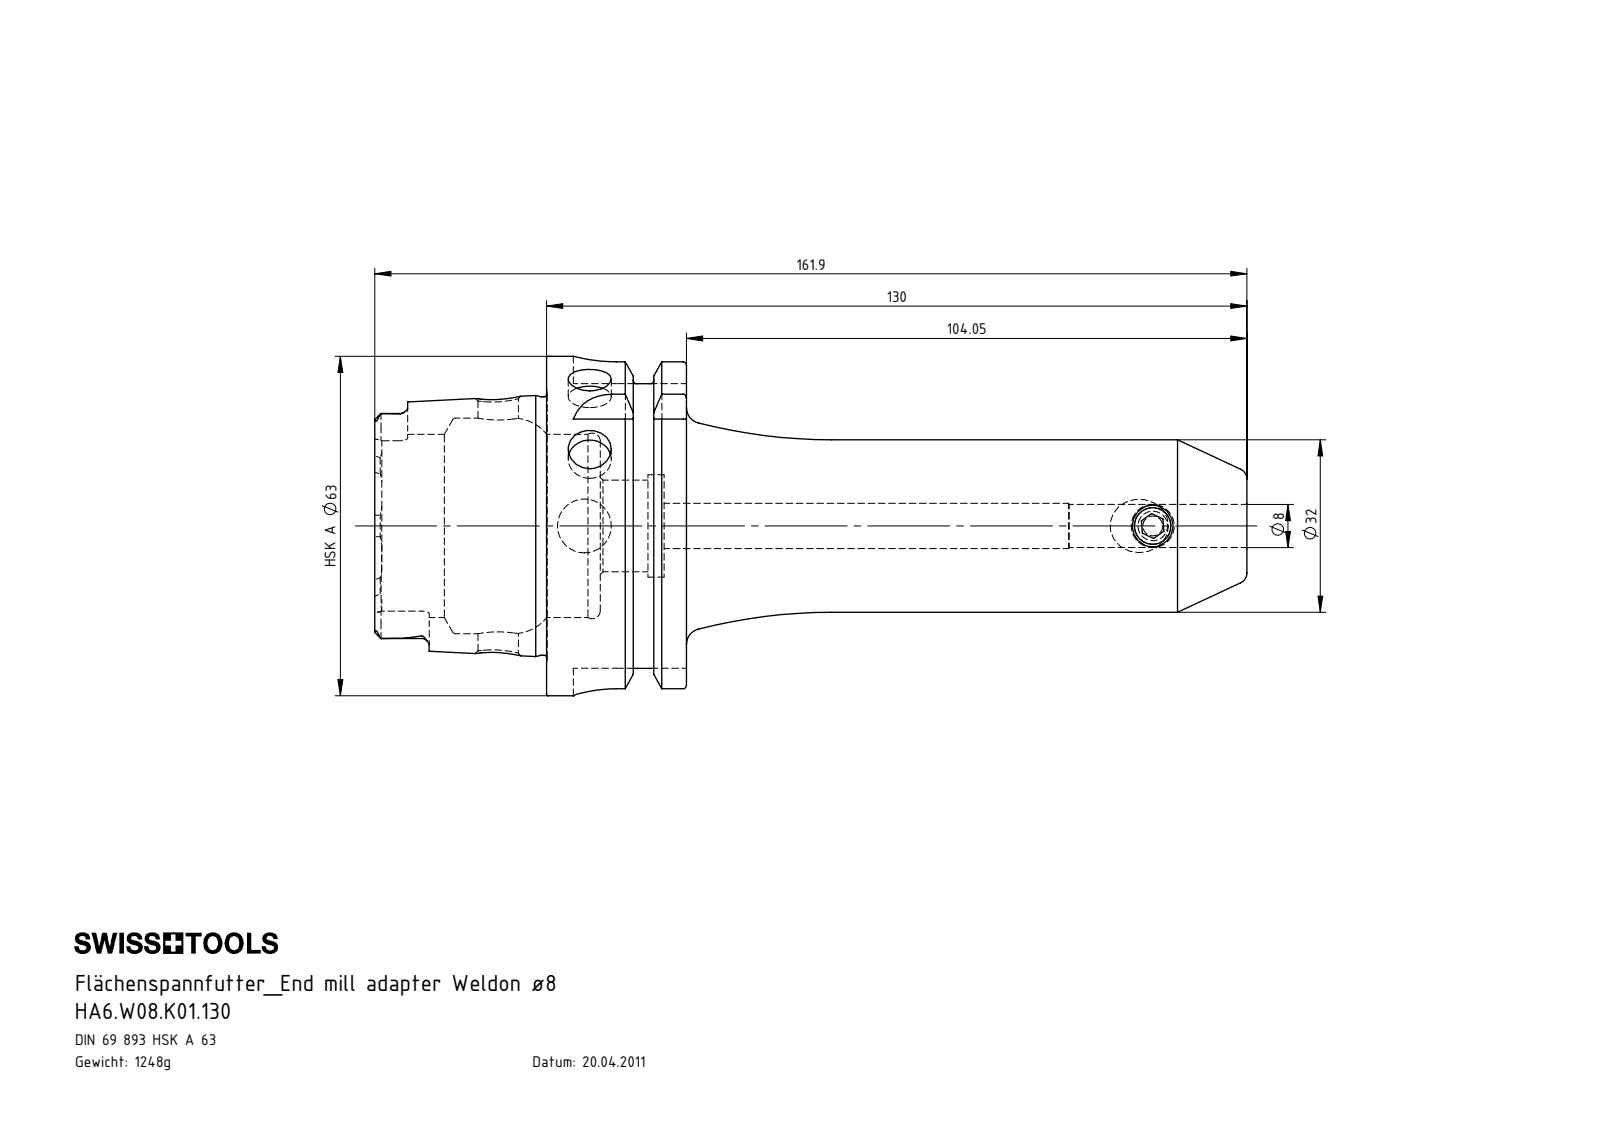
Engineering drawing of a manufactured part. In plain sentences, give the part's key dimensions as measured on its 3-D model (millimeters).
The part is named "HA6-W08.K01.130; W08-ER1.001.010; HA6-W08.K01.130_A_Fertigbearbeitung". Its 3-D file was written by "SolidWorks 2012 (CONFIG_CONTROL_DESIGN)". It is 2 solids with 203 faces: 57 planar, 55 cylindrical and 91 other. Overall it measures 161.9 by 63 by 63 millimeters. Its volume is 159 027 cubic millimeters and its surface area 35 308 square millimeters. Round holes: 3 of diameter 8, 1 of diameter 6.8, 1 of diameter 7.5, 1 of diameter 8.4, 1 of diameter 10, 1 of diameter 17, 1 of diameter 19, 1 of diameter 34, 1 of diameter 40. Round bosses or shafts: 1 of diameter 63, 1 of diameter 54.95, 1 of diameter 47.94, 1 of diameter 32, 1 of diameter 8. Partial cylindrical surfaces (rounded edges, fillets, slot ends): 6 of radius 1.4, 4 of radius 2.88, 4 of radius 8. The main face-to-face distances are 25.95, 16, 9.95, 31.9, 41.85, 57.85, 52.8, 21.8, 11.85, 53.7. The hole center spacings are 105.5.
